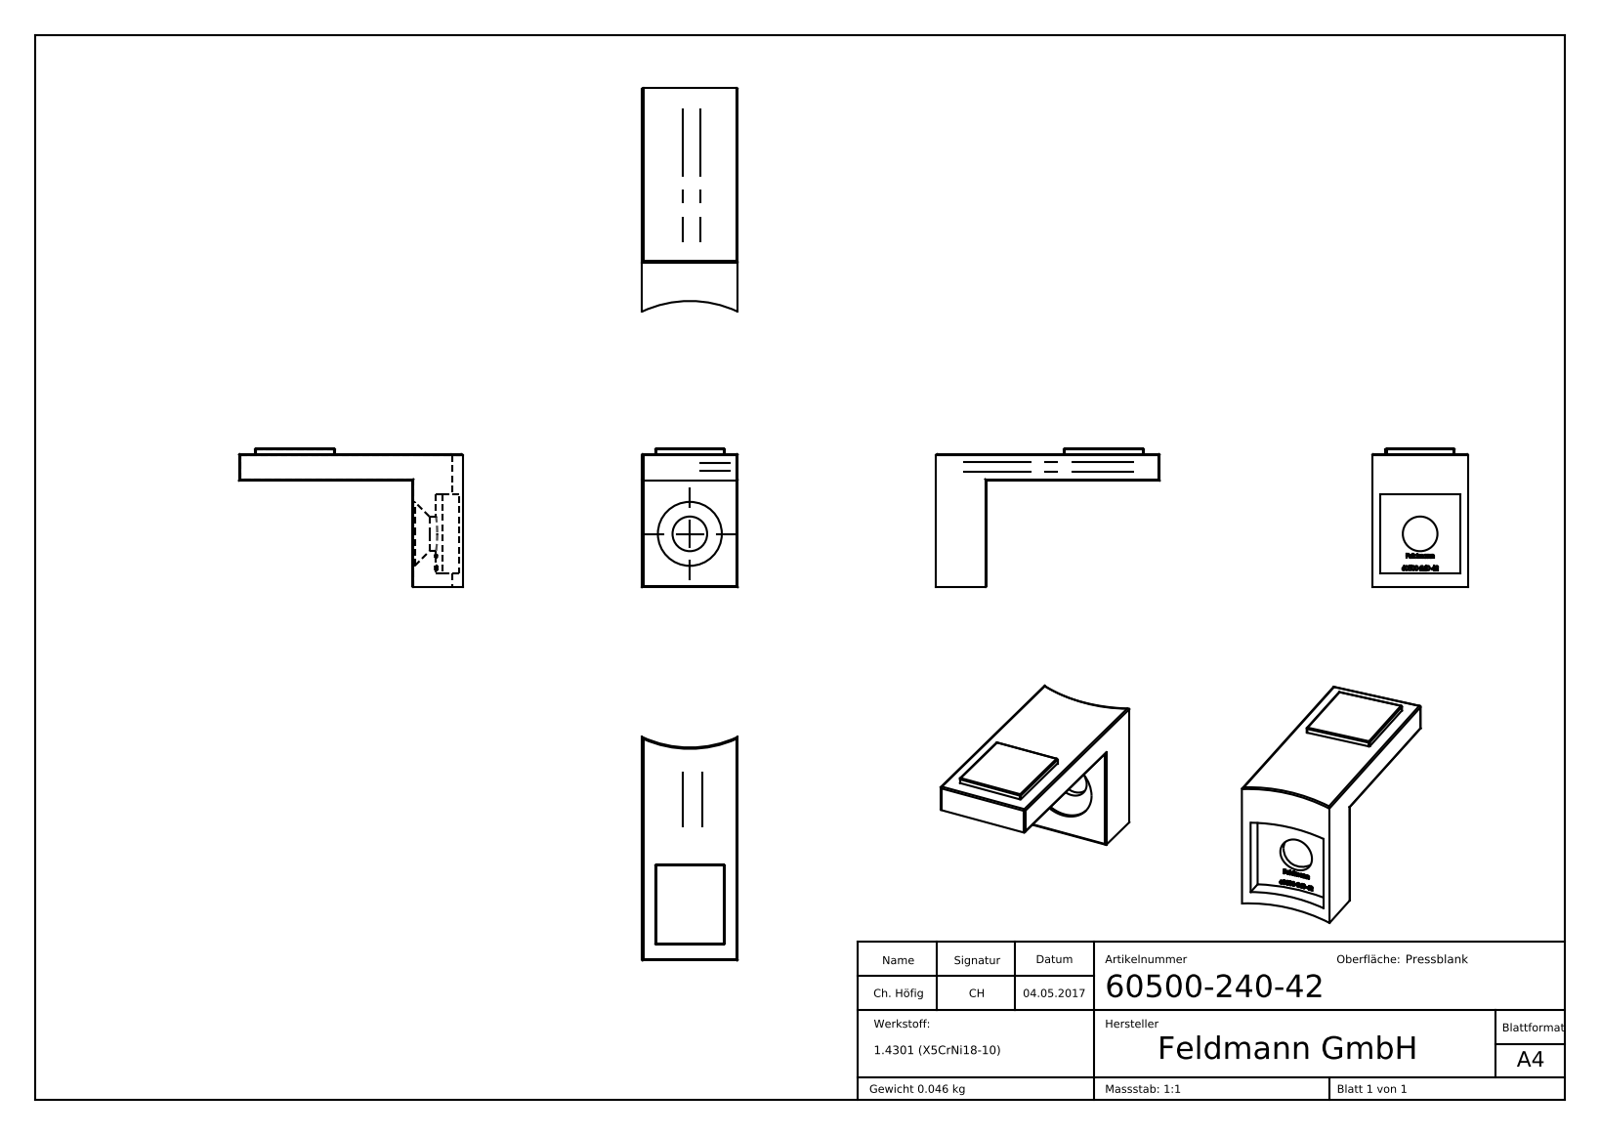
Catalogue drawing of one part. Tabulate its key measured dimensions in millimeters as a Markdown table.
| quantity | value |
| --- | --- |
| part name | 60500-240-42 |
| STEP written by | SolidWorks 2015 (CONFIG_CONTROL_DESIGN) |
| units | millimeters |
| bodies | 2 solids, 303 faces (126 planar, 57 cylindrical, 120 other) |
| overall size | 42.01 × 26 × 18 |
| volume | 5 808 mm³ |
| surface area | 3 798 mm² |
| round holes (diameter × count) | 6.5 × 1, 12 × 1 |
| partial cylindrical surfaces (radius × count) | 0.25 × 10, 0.2 × 8, 21.2 × 1, 24.2 × 1, 24.3 × 1 |
| main face-to-face distances | 5, 18, 1, 6, 20, 25, 26, 2.5, 15, 1.5 |
